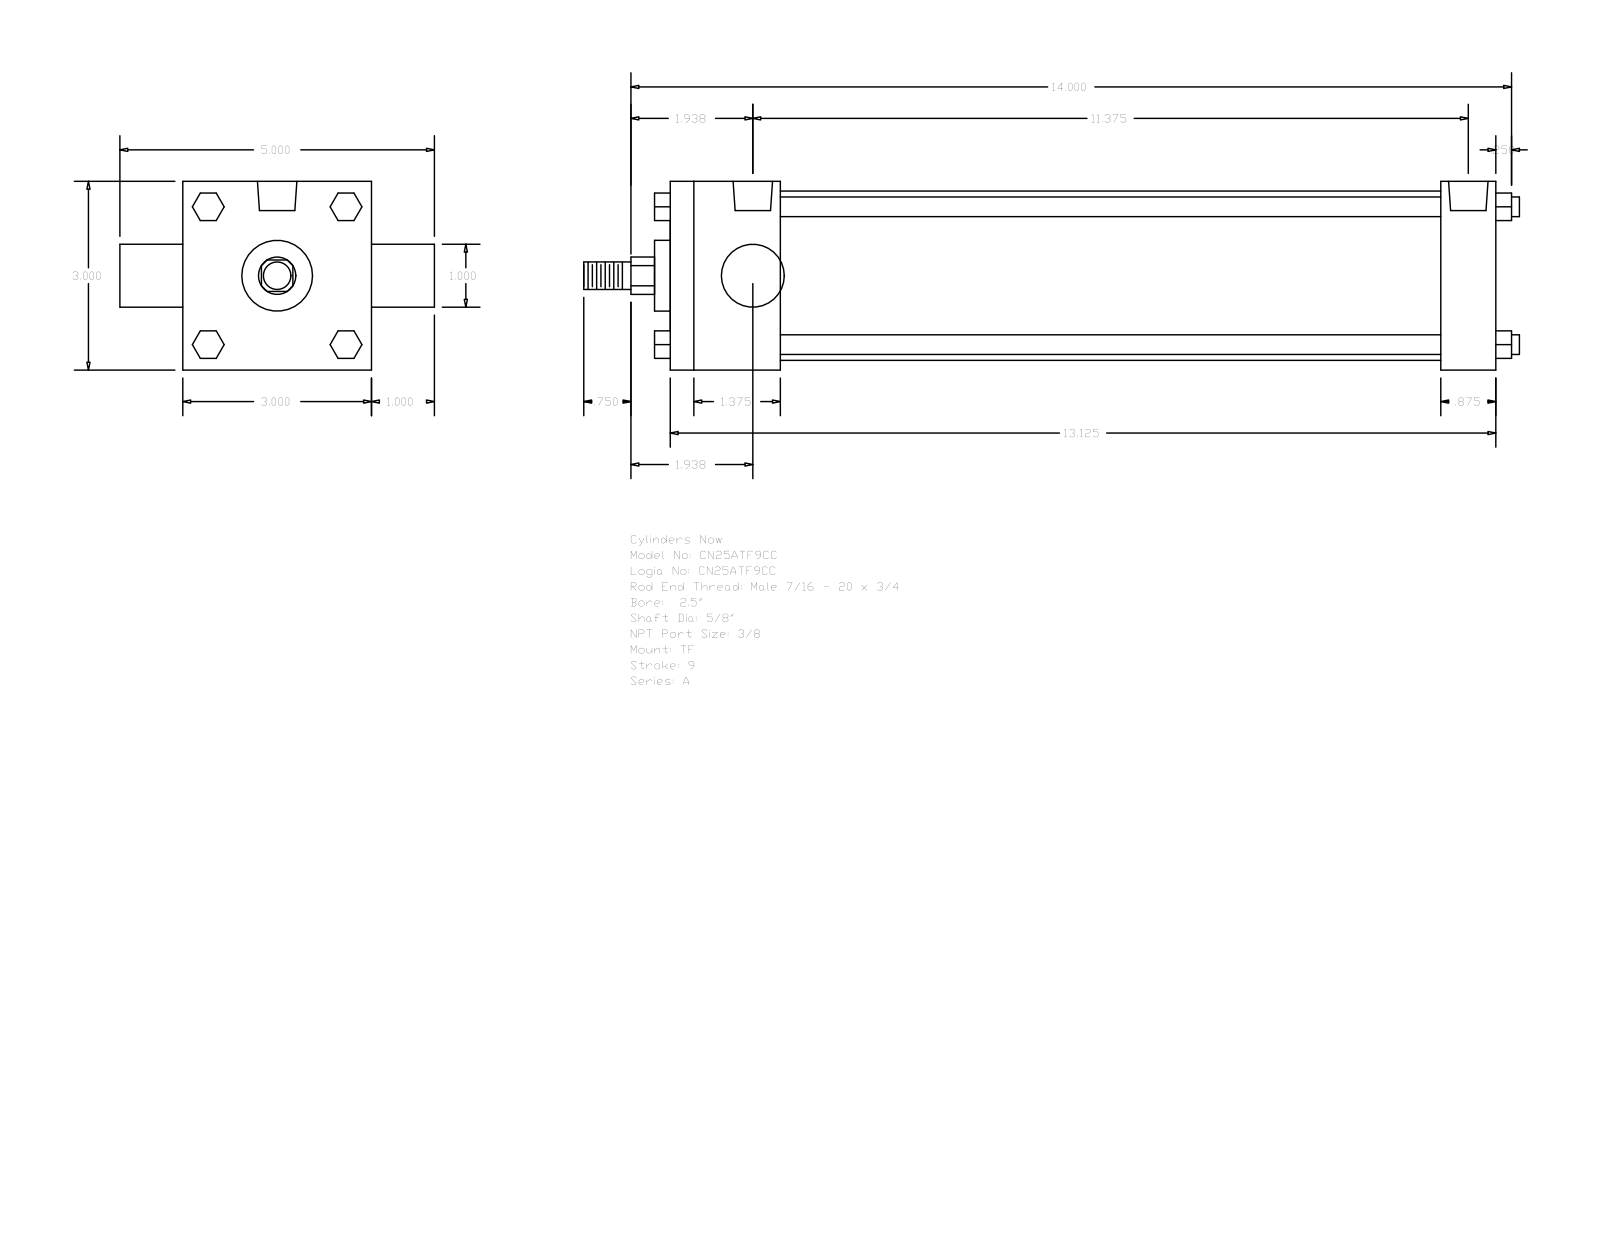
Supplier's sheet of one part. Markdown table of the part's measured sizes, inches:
| quantity | value |
| --- | --- |
| part name | A_TF__0250_0.625 |
| STEP written by | GSSL Pune (CONFIG_CONTROL_DESIGN) |
| units | inches |
| bodies | 0 solids, 120 faces (92 planar, 28 cylindrical, 0 other) |
| overall size | 14.875 × 5 × 3 |
| round holes (diameter × count) | 0.219 × 3, 0.627 × 2 |
| round bosses / shafts (diameter × count) | 0.313 × 4, 2.69 × 1, 1.125 × 1, 1 × 1, 0.625 × 1, 0.437 × 1 |
| partial cylindrical surfaces (radius × count) | 0.297 × 1 |
| main face-to-face distances | 3, 13.125, 1.75, 12.25, 10.5, 11.375, 0.875, 1, 4, 0.25 |
| hole center spacings | 0.094, 11.469, 11.375, 11.563 |
